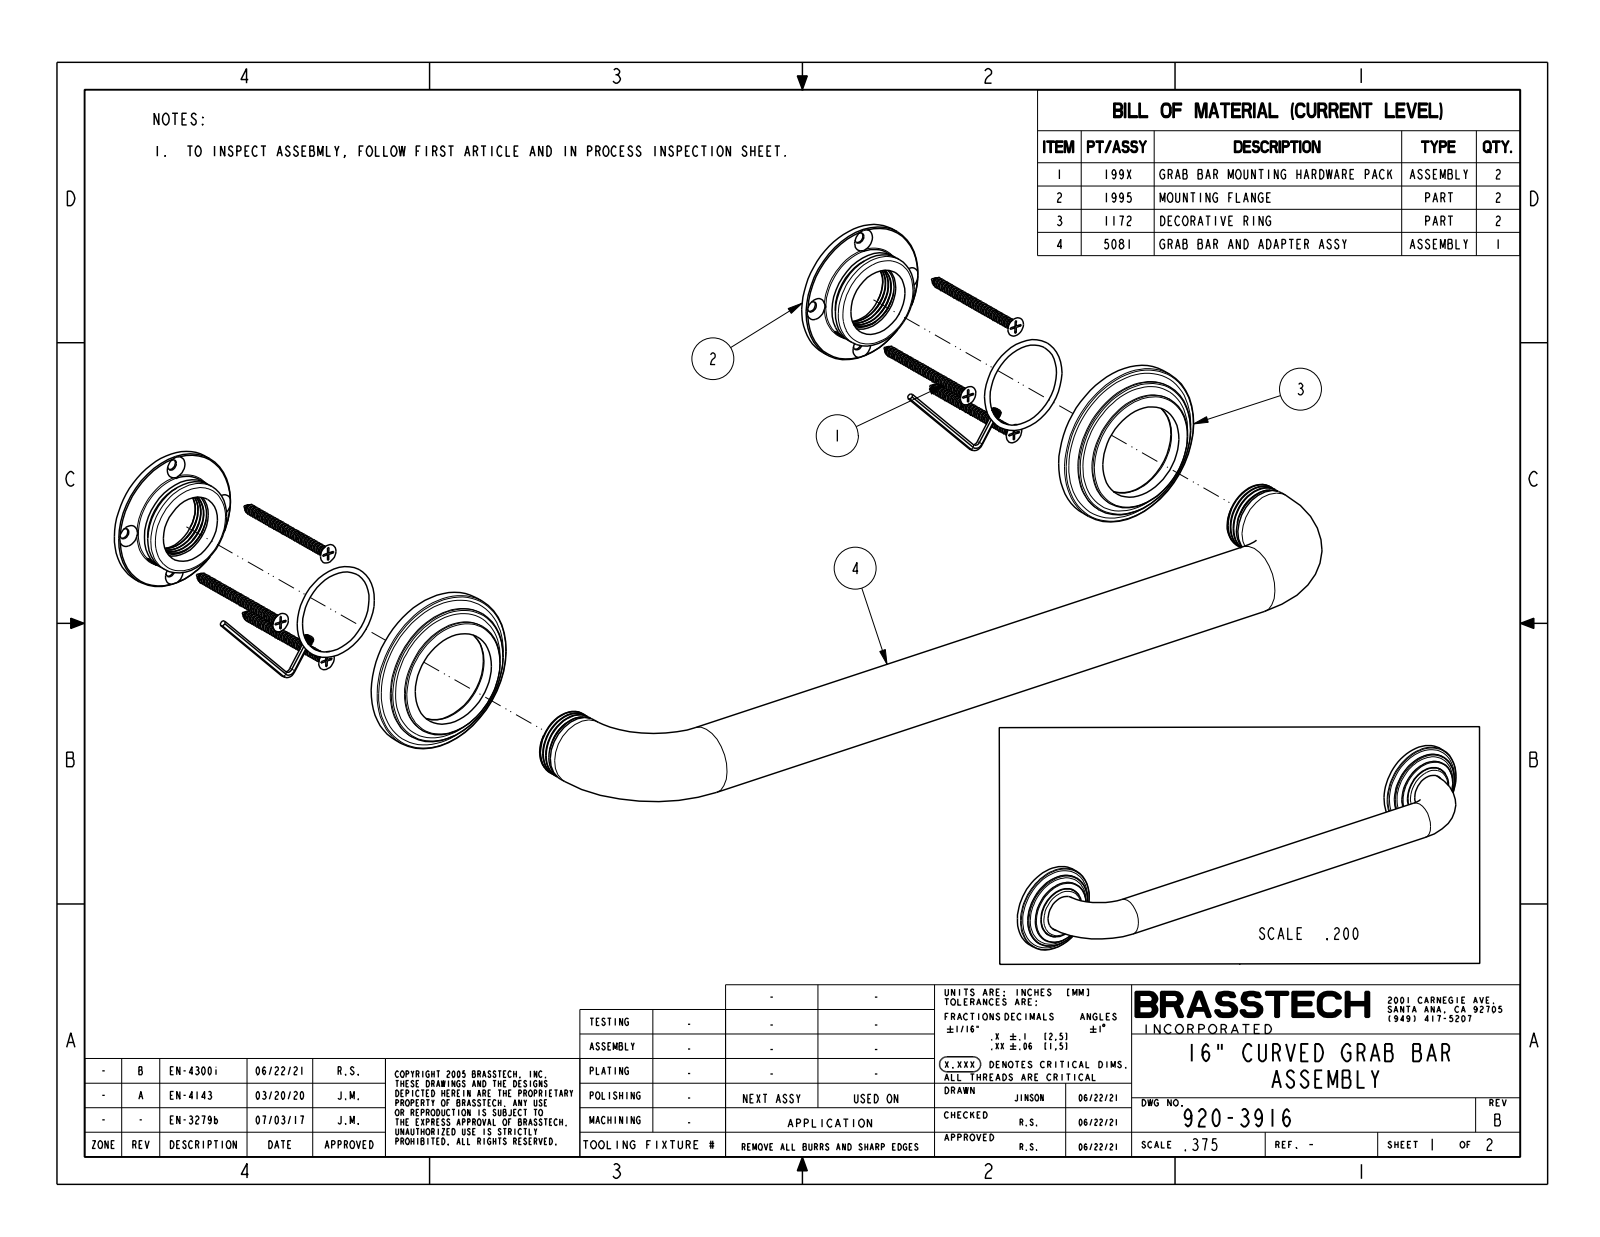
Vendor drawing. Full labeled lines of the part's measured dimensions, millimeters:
Part name (STEP PRODUCT): 91496; 1995; 20-287_ASM; 80527 (+4 more)
STEP written by: PRO/ENGINEER BY PARAMETRIC TECHNOLOGY CORPORATION, 2013150 (CONFIG_CONTROL_DESIGN)
Units: millimetres
Bodies: 9 solids, 684 faces (160 planar, 204 cylindrical, 320 other)
Overall size (bounding box): 482.6 × 76.2 × 69.9
Volume: 120 300 mm³ · Surface area: 202 600 mm²
Round holes (diameter × count): ⌀5.1 ×8, ⌀29.3 ×3, ⌀4.1 ×2, ⌀22 ×2, ⌀29.5 ×2, ⌀32 ×2, ⌀45 ×2, ⌀72.2 ×2
Round bosses / shafts (diameter × count): ⌀31.8 ×3, ⌀76.2 ×2, ⌀66 ×2, ⌀55.9 ×2, ⌀49 ×2, ⌀44.5 ×2, ⌀40.5 ×2, ⌀31.4 ×2
Partial cylindrical surfaces — rounded edges, fillets, slot ends (radius × count): R5.4 ×8, R1 ×2
Main face-to-face distances: 3.8, 9.5, 13.3, 1.9, 11.4, 4.2, 15.2, 8.9, 2.5, 6.1
Hole centre spacings: 27.6, 39.1, 406.4, 55.2, 379.8, 407.3, 434.9, 378.8
